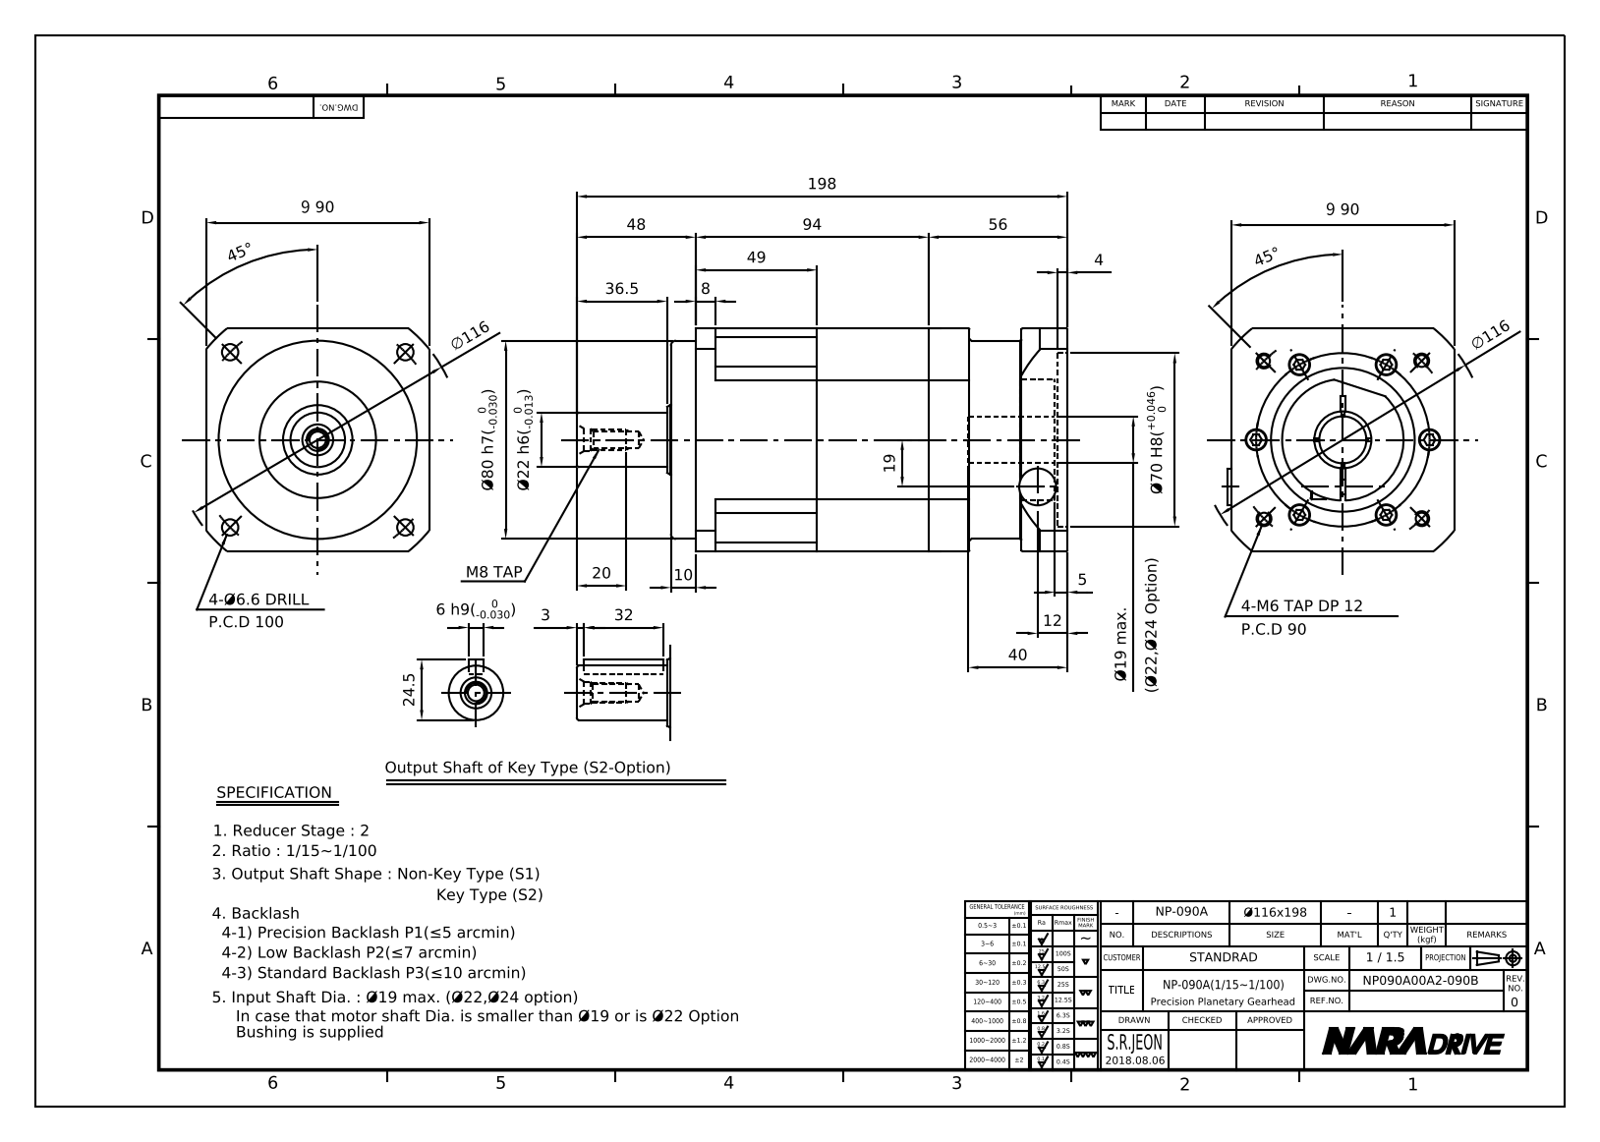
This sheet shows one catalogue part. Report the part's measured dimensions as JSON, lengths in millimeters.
{"part_name": "NP090A00A2-090B-S1", "step_written_by": "Autodesk Inventor 2015 (AUTOMOTIVE_DESIGN)", "units": "millimeters", "bodies": {"solids": 2, "faces": 444, "planar": 204, "cylindrical": 128, "other": 112}, "overall_size": [198, 91.5, 90], "volume_mm3": 684205, "surface_area_mm2": 133147, "round_holes": [[9, 11], [4.13, 10], [5.5, 10], [4.92, 5], [6.6, 5], [6.65, 1], [7, 1], [8.5, 1], [19, 1], [23, 1], [28, 1], [47, 1]], "round_bosses_or_shafts": [[8.5, 10], [5, 10], [80, 1], [79, 1], [49, 1], [22, 1], [15, 1], [10, 1]], "partial_cylinders_radius": [[0.5, 16], [10, 4], [5.5, 1], [35, 1], [51, 1], [58, 1]], "face_to_face_distances": [90, 51, 104, 160, 109, 8, 10, 41, 56, 94], "hole_center_spacings": [35, 60.62, 14.4, 31.98, 45, 49.34, 63.64, 63.76]}
